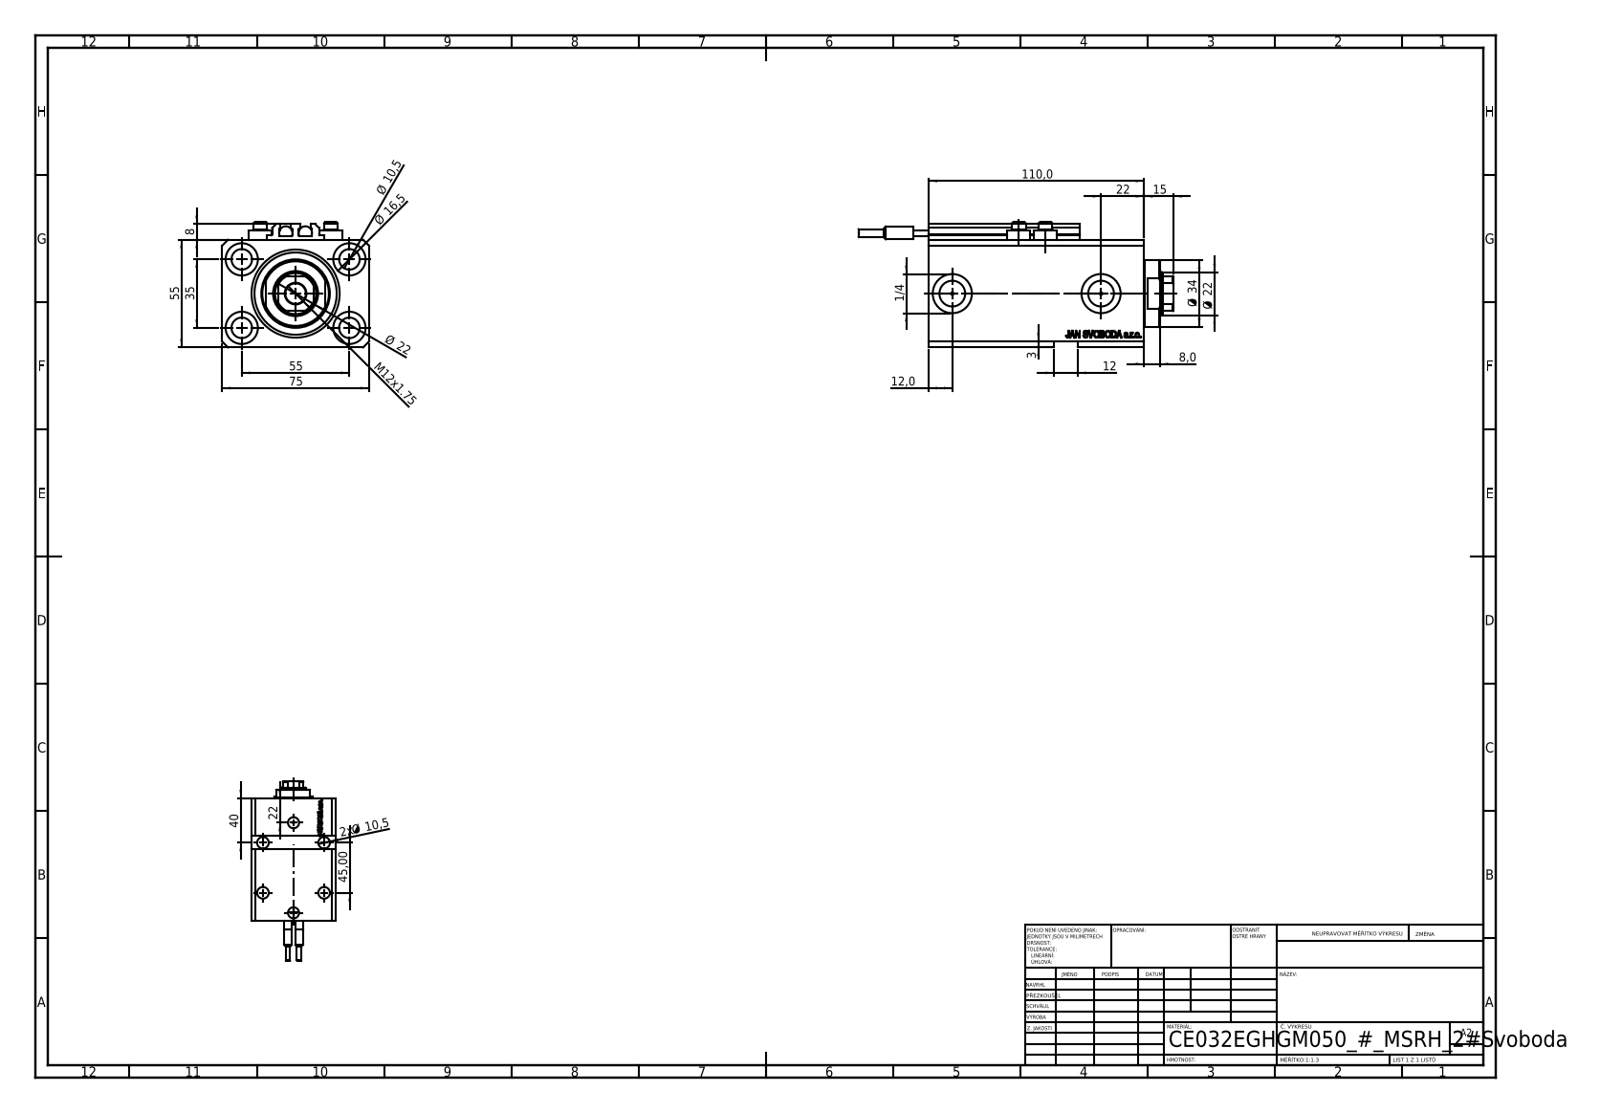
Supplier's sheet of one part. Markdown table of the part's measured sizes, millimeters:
| quantity | value |
| --- | --- |
| part name | V250CE_C_VCP; SWITCH_V250CE; V250CE_E_Body; ALLEN BOLT V250CE (+1 more) |
| STEP written by | SolidWorks 2019 (CONFIG_CONTROL_DESIGN) |
| units | millimeters |
| bodies | 10 solids, 1136 faces (546 planar, 158 cylindrical, 432 other) |
| overall size | 161 × 75 × 64 |
| volume | 384 911 mm³ |
| surface area | 98 392 mm² |
| round holes (diameter × count) | 10.5 × 9, 1.25 × 4, 4 × 4, 16.5 × 4, 10 × 2, 13.16 × 2, 20 × 2, 22 × 1, 32 × 1, 45 × 1 |
| round bosses / shafts (diameter × count) | 11.6 × 4, 7 × 4, 6.8 × 2, 6.5 × 2, 4 × 2, 34 × 1 |
| partial cylindrical surfaces (radius × count) | 0.2 × 10, 10.5 × 1 |
| main face-to-face distances | 55, 75, 3, 15, 110, 57, 95, 9.9, 85.1, 100.1 |
| hole center spacings | 32.6, 32.87, 55, 68.74, 13.6, 14.09, 23.05, 25.81 |
